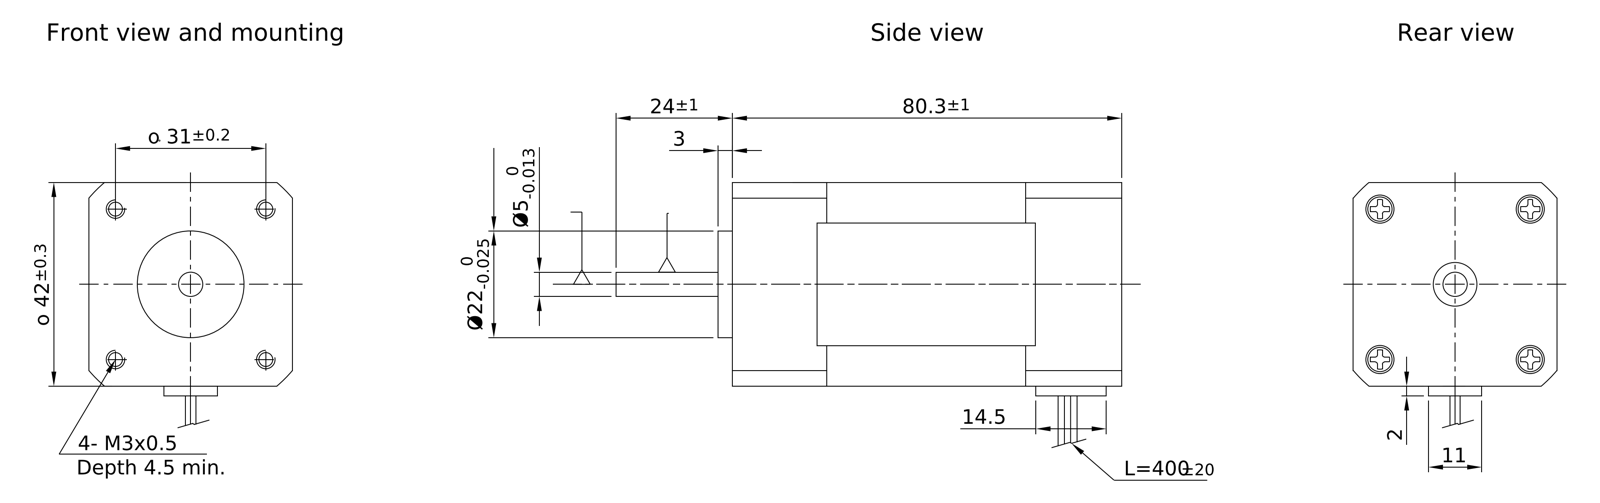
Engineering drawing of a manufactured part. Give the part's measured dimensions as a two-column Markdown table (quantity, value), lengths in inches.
| quantity | value |
| --- | --- |
| part name | DB41L024030-A |
| STEP written by | Autodesk Inventor 2016 (AUTOMOTIVE_DESIGN) |
| units | inches |
| bodies | 16 solids, 262 faces (133 planar, 57 cylindrical, 72 other) |
| overall size | 4.108 × 2.835 × 1.654 |
| volume | 8.355 in³ |
| surface area | 45.19 in² |
| round holes (diameter × count) | 0.097 × 4, 0.106 × 4, 0.228 × 4, 0.197 × 1, 0.236 × 1, 0.354 × 1 |
| round bosses / shafts (diameter × count) | 0.059 × 8, 0.098 × 4, 0.089 × 4, 0.866 × 1 |
| partial cylindrical surfaces (radius × count) | 0.217 × 1, 0.965 × 1, 1.083 × 1 |
| main face-to-face distances | 1.654, 2.067, 2.768, 0.701, 0.394, 2.461, 3.161, 0.118, 2.579, 0.079 |
| hole center spacings | 0.863, 1.22, 1.726 |
